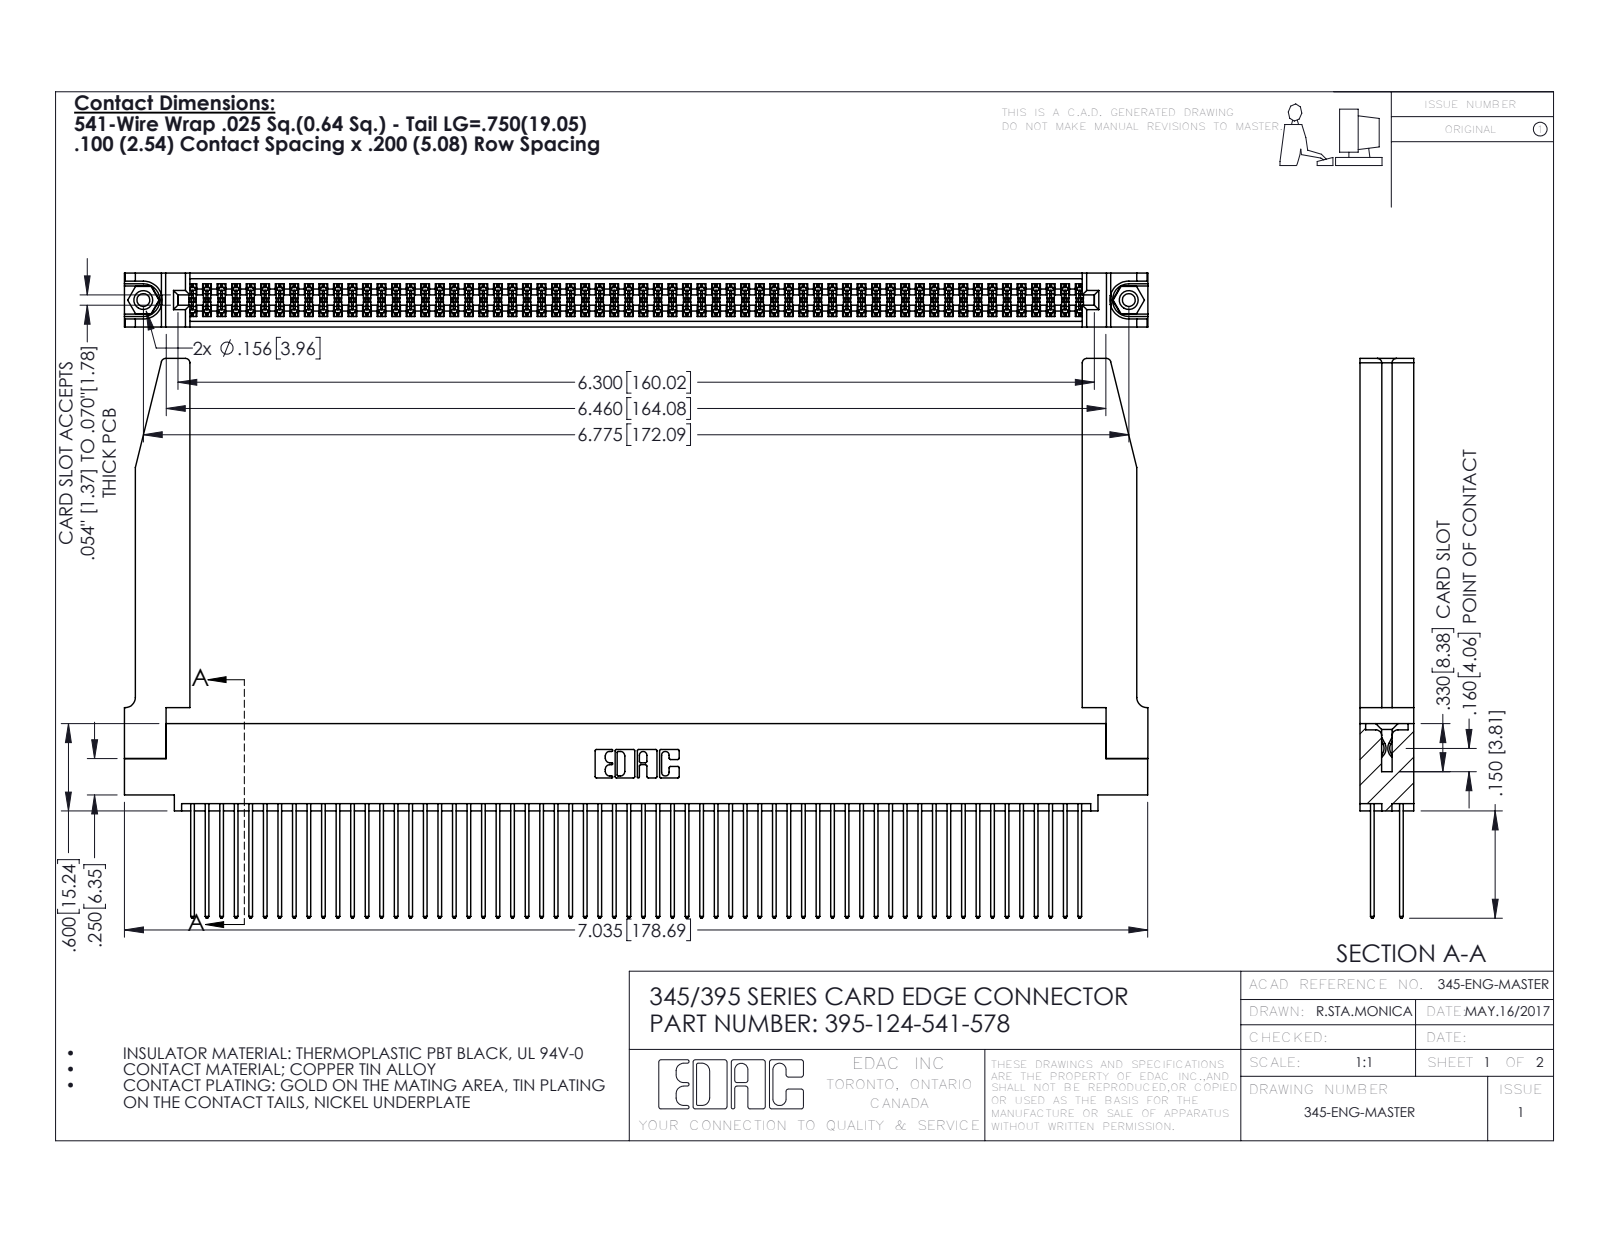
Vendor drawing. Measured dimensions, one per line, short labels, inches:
name: 345 Part_0.110 Offset - 0.156 Dia-TH; 345-250-001_345-250-001-102; 395-124-541-578; 345-220-078_345-220-078 (+1 more)
written by: SolidWorks 2016 (CONFIG_CONTROL_DESIGN)
unit: in
bodies: 129 solids, 6564 faces (4318 planar, 2194 cylindrical, 52 other)
size: 7.036 × 3.847 × 0.37
volume: 1.584 in³; area: 58.19 in²
holes: 2× ⌀0.089, 2× ⌀0.125, 2× ⌀0.156, 1× ⌀0.064
bosses: 2× ⌀0.155
rounds: 186× R0.006, 124× R0.01, 22× R0.01, 8× R0.03, 6× R0.007, 6× R0.031, 3× R0.026, 2× R0.014
face distances: 0.072, 0.298, 0.098, 0.272, 0.025, 0.2, 0.37, 0.225, 0.175, 0.148
hole spacings: 0.27, 6.539, 6.775
